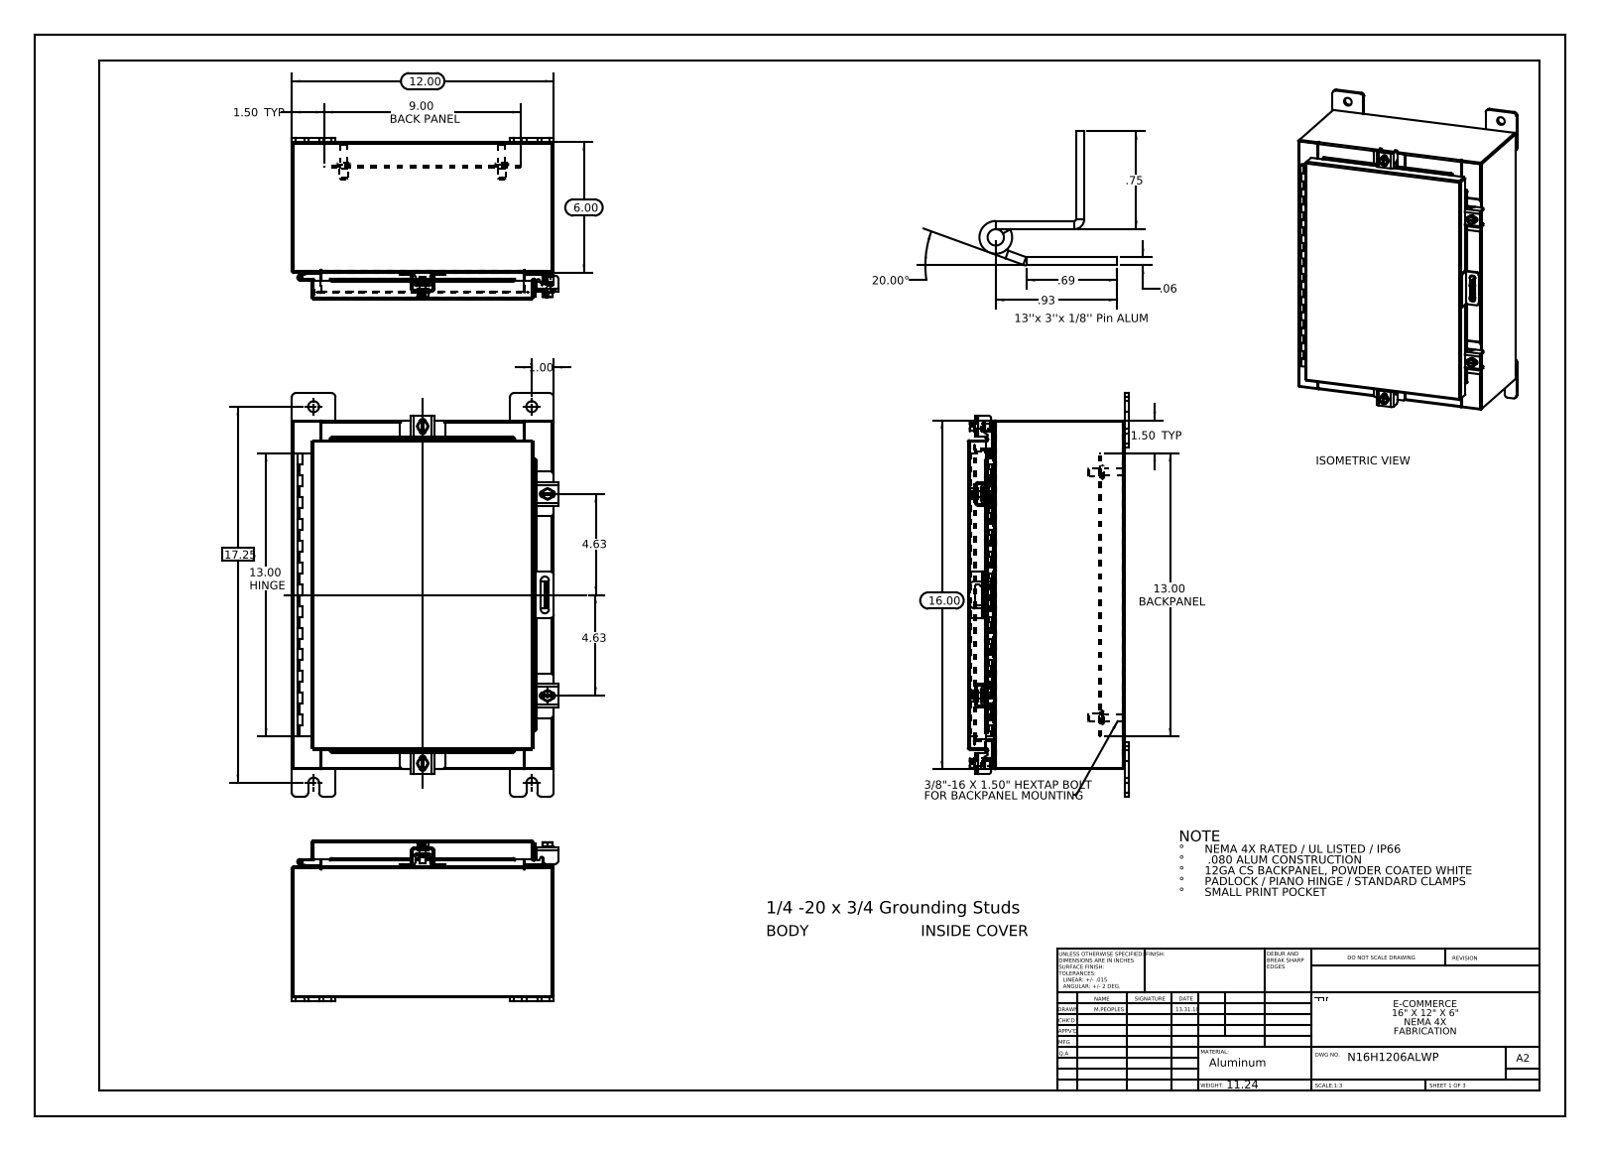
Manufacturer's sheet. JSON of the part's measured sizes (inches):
{"part_name": "N16H1206ALWP Mounting Feet; N16H1206ALWP Clamp Bracket; N16H1206ALWP Padlock Hasp; N16H1206ALWP Backpanel (+8 more)", "step_written_by": "SolidWorks 2013 (CONFIG_CONTROL_DESIGN)", "units": "inches", "bodies": {"solids": 37, "faces": 1267, "planar": 680, "cylindrical": 507, "other": 80}, "overall_size": [18.5, 12.211, 7.389], "volume_in3": 81.37, "surface_area_in2": 2072, "round_holes": [[0.5, 8], [0.213, 4], [0.26, 4], [0.125, 2], [0.125, 1]], "round_bosses_or_shafts": [[0.25, 5], [0.625, 4], [0.5, 4], [0.399, 4], [0.375, 4], [0.33, 4]], "partial_cylinders_radius": [[0.19, 24], [0.013, 23], [0.06, 22], [0.088, 21], [0.125, 10], [0.12, 8], [0.141, 8], [0.05, 7]], "face_to_face_distances": [0.075, 7.126, 11.925, 7.201, 7.051, 15.925, 5.925, 1.201, 1, 1.075], "hole_center_spacings": [13.834, 2.225, 2.327, 3.3, 4.189, 4.19, 5.012, 5.08]}
